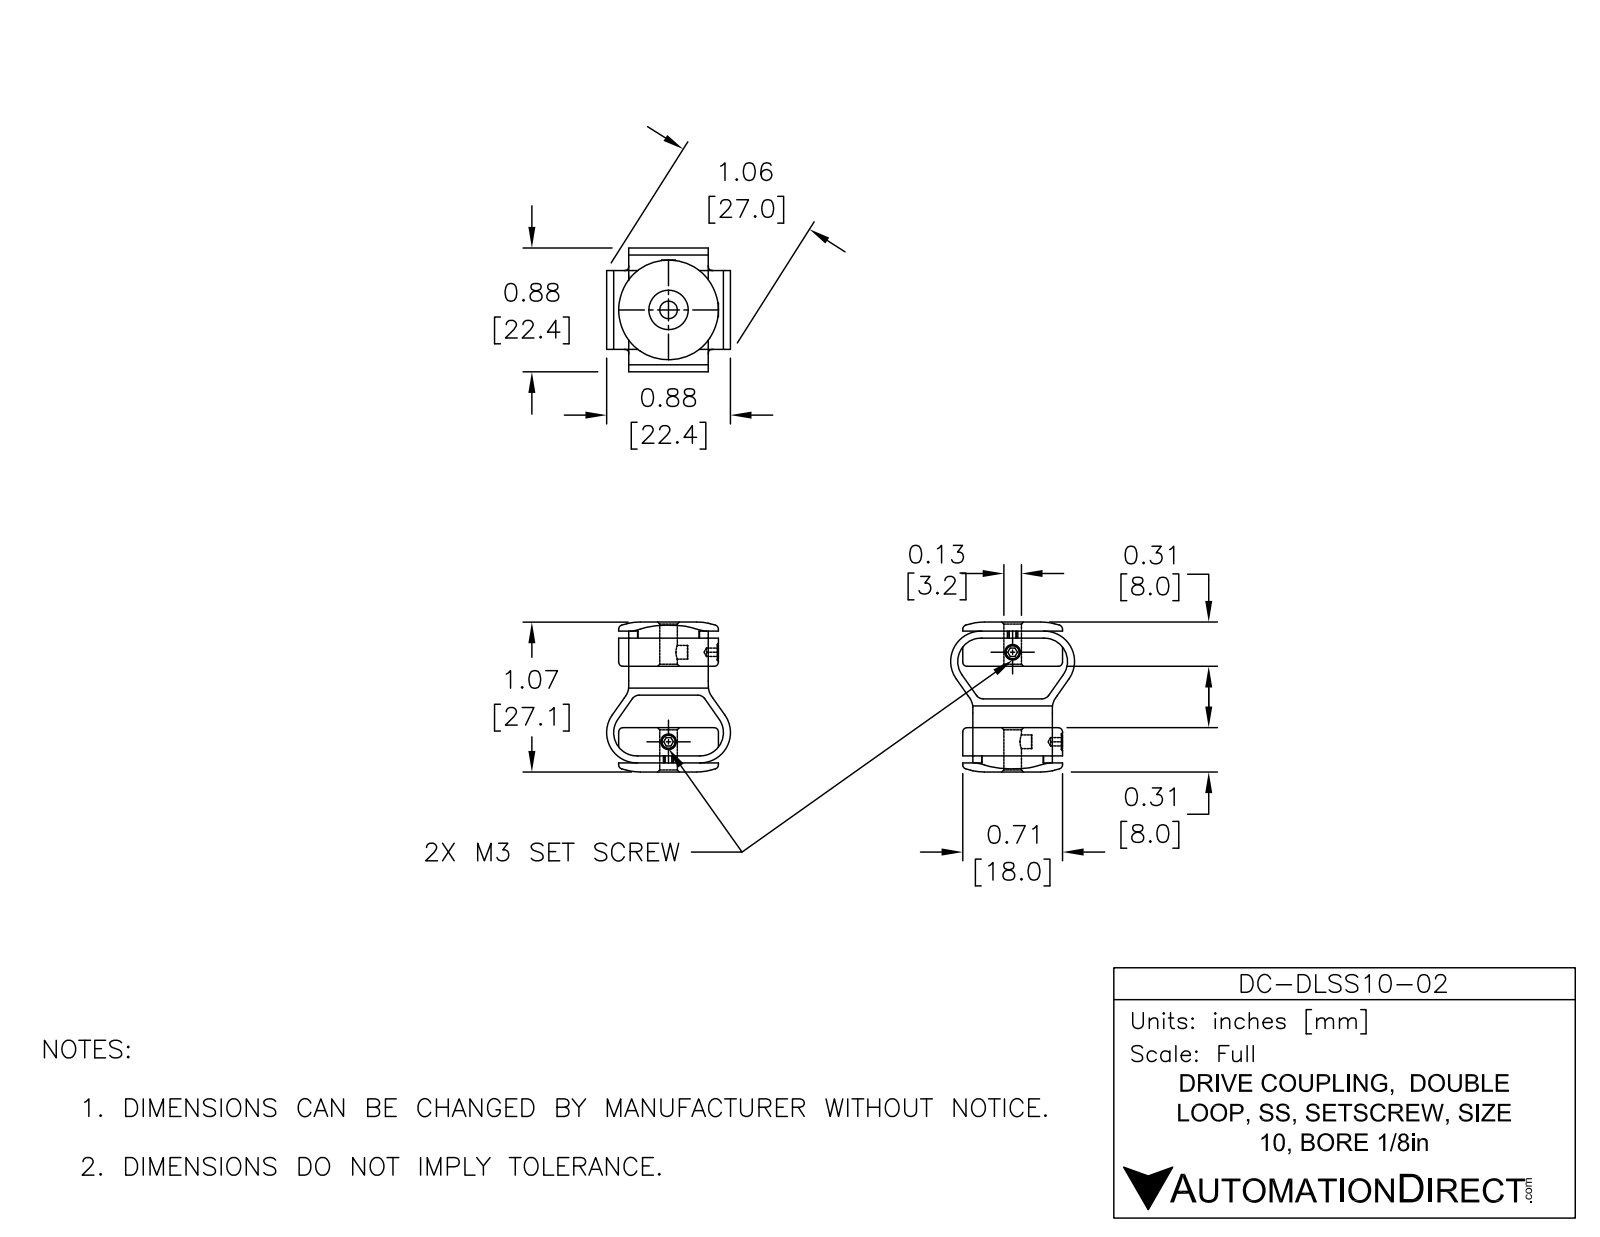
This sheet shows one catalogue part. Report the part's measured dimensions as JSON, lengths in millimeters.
{"part_name": "DC-DLSS10-02", "step_written_by": "SolidWorks 2015 (AUTOMOTIVE_DESIGN)", "units": "millimeters", "bodies": {"solids": 1, "faces": 110, "planar": 57, "cylindrical": 28, "other": 25}, "overall_size": [33.4, 22.35, 22.35], "volume_mm3": 4480, "surface_area_mm2": 3915, "round_holes": [[3.18, 1]], "round_bosses_or_shafts": [[18.01, 1]], "partial_cylinders_radius": [[4.19, 4], [5.46, 4], [5.59, 1]], "face_to_face_distances": [1.27, 33.4, 16.38, 17.02, 17.65, 15.75, 7.06, 26.34, 9.96, 9.32]}
